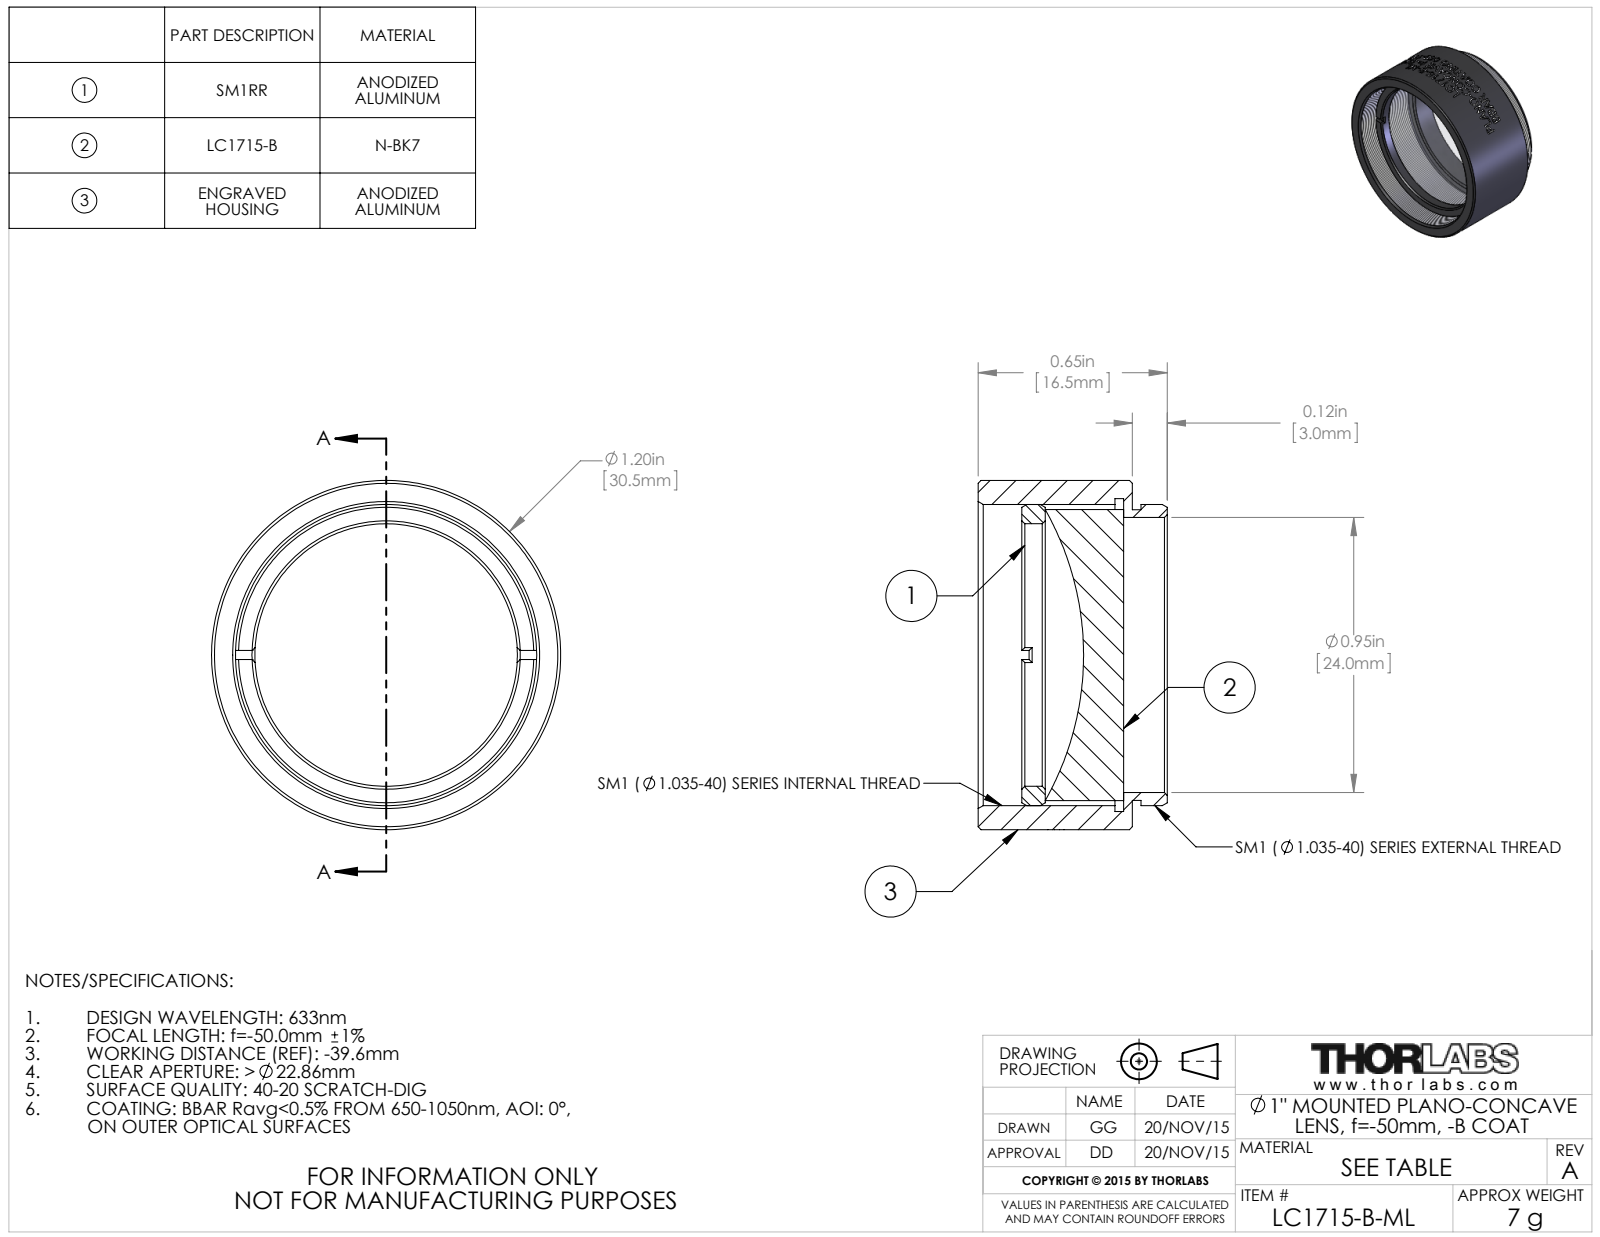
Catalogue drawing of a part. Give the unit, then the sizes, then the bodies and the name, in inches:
Units: inches
Overall size (bounding box): 1.2 × 1.2 × 0.65
Round holes (diameter × count): ⌀0.902 ×1, ⌀0.945 ×1, ⌀1.075 ×1
Round bosses / shafts (diameter × count): ⌀1.2 ×1, ⌀1.035 ×1, ⌀1 ×1, ⌀0.999 ×1
Main face-to-face distances: 0.03, 0.03, 0.5, 0.53, 0.5, 0.15, 0.3, 0.27, 0.27, 0.23
Volume: 0.344 in³ · Surface area: 8.744 in²
Bodies: 3 solids, 152 faces (20 planar, 108 cylindrical, 24 other)
Part name (STEP PRODUCT): TTN045280-E0W
STEP written by: SolidWorks 2014 (CONFIG_CONTROL_DESIGN)
